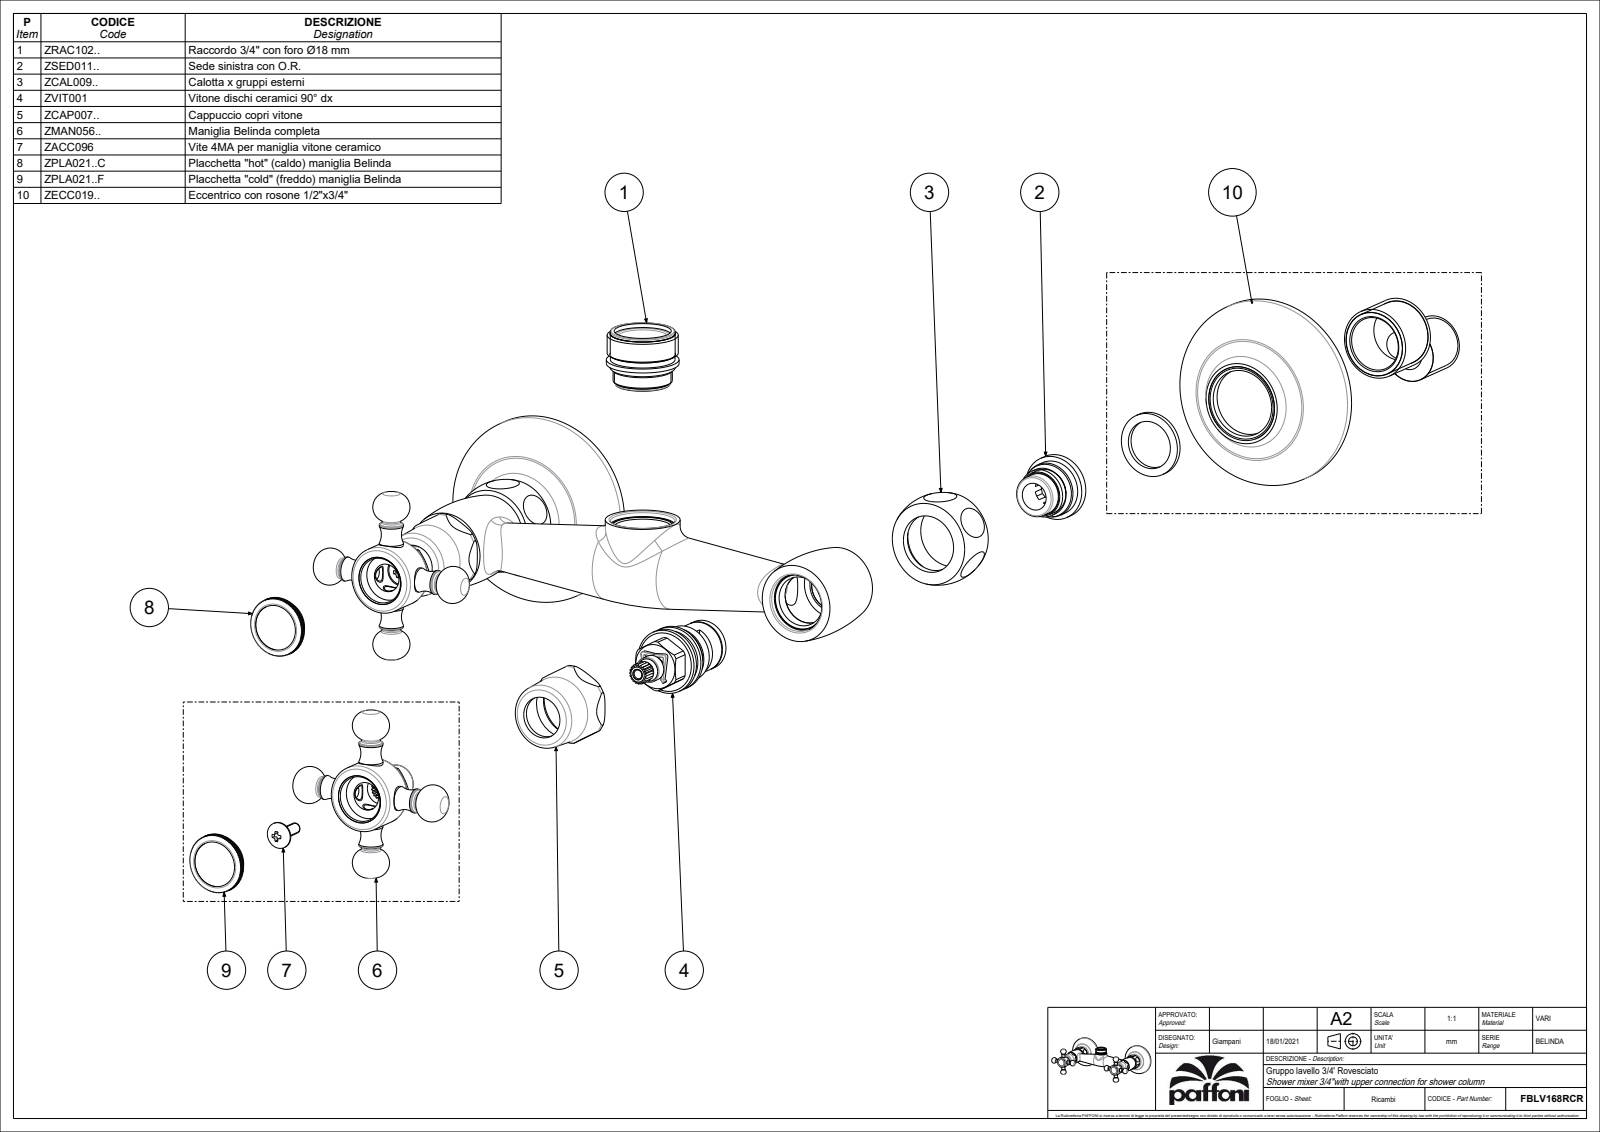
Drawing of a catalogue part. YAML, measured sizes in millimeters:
part_name: "FBLV168RCR"
step_written_by: "CREO PARAMETRIC BY PTC INC, 2020044 (CONFIG_CONTROL_DESIGN)"
units: millimeters
bodies: {solids: 3, faces: 1080, planar: 500, cylindrical: 320, other: 260}
overall_size: [220, 123.7, 70]
volume: 141674
surface_area: 77889
round_holes:
  - {diameter: 16.5, count: 2}
  - {diameter: 18.6, count: 2}
  - {diameter: 19, count: 2}
  - {diameter: 21.5, count: 2}
  - {diameter: 25, count: 2}
  - {diameter: 68, count: 2}
  - {diameter: 18.2, count: 1}
  - {diameter: 21, count: 1}
  - {diameter: 21.2, count: 1}
round_bosses_or_shafts:
  - {diameter: 9, count: 3}
  - {diameter: 7, count: 3}
  - {diameter: 70, count: 2}
  - {diameter: 28.14, count: 2}
  - {diameter: 14, count: 2}
  - {diameter: 13, count: 2}
  - {diameter: 27.8, count: 1}
  - {diameter: 27, count: 1}
partial_cylinders:
  - {radius: 11, count: 2}
  - {radius: 5.25, count: 1}
face_to_face_distances: [17.5, 50.69, 33.19, 86, 18, 68.5, 35.31, 7, 0.5, 25]
hole_center_spacings: [150]
